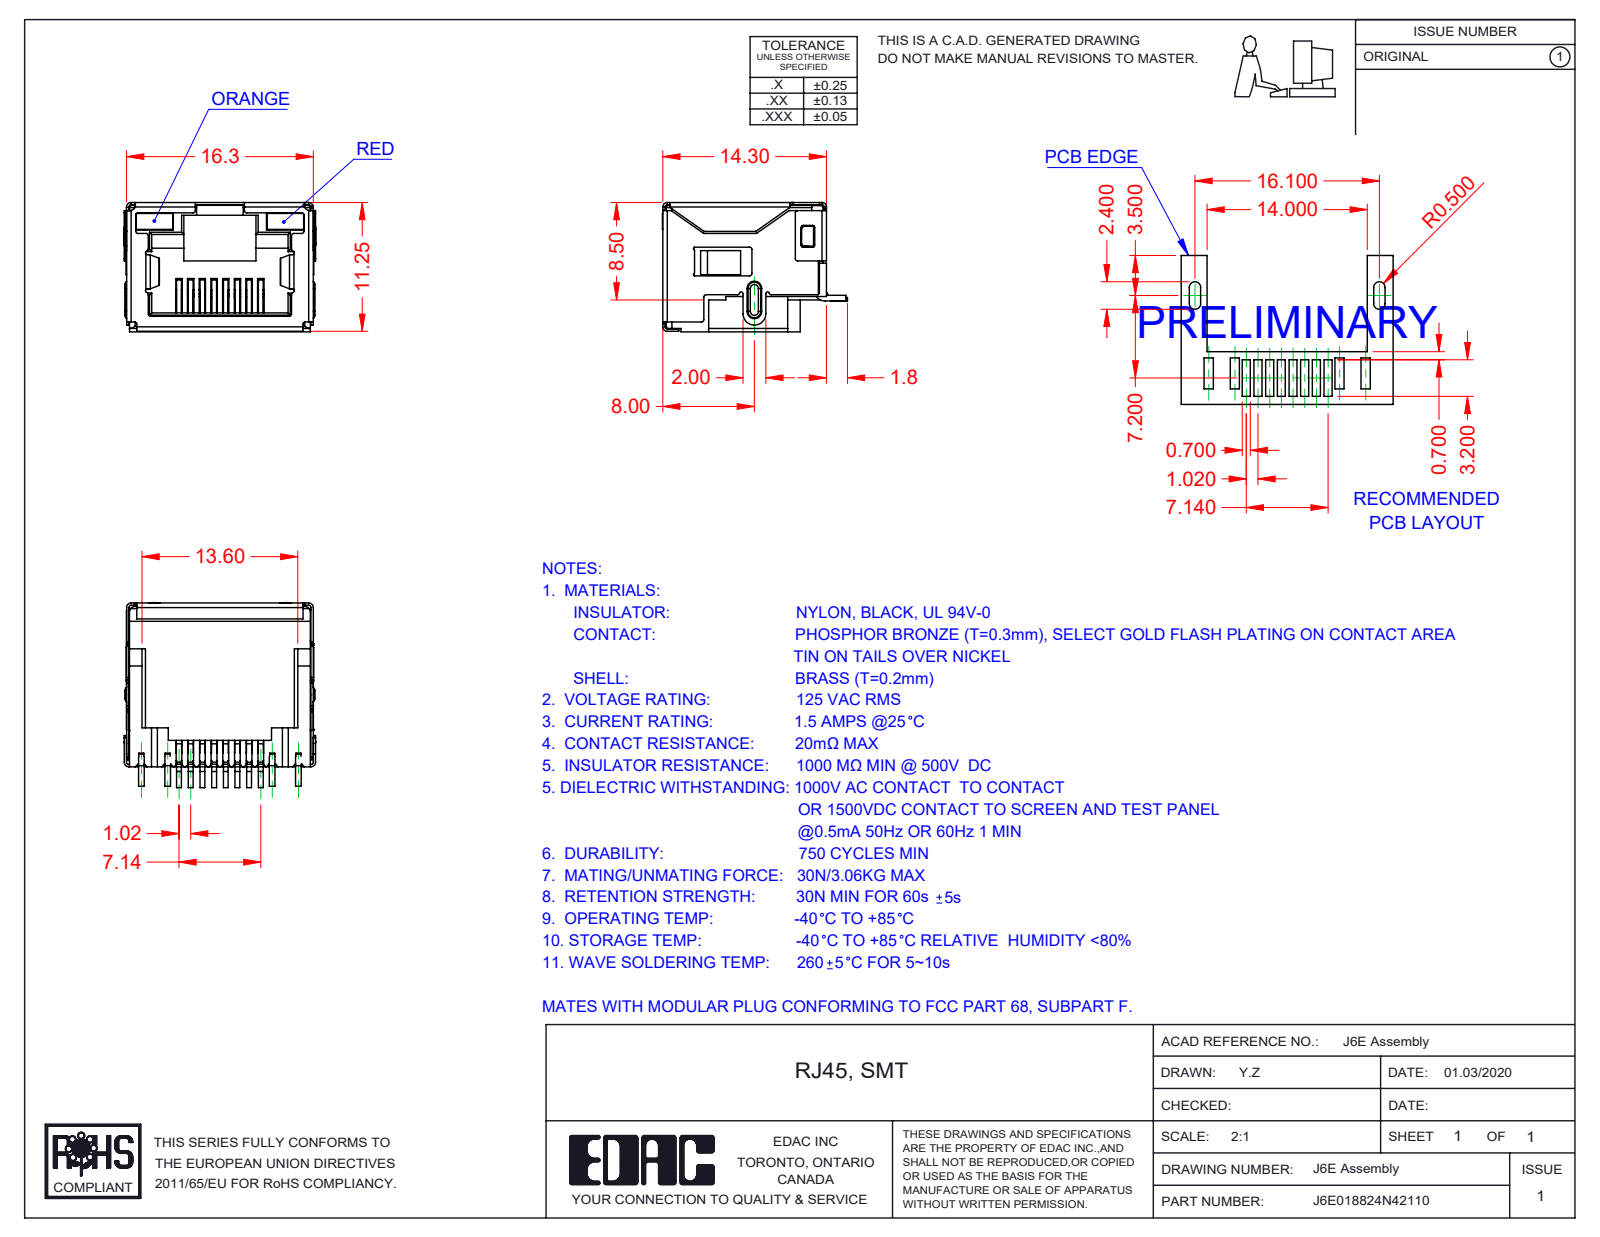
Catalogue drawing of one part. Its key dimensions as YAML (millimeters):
part_name: "6E LED LH_4-Orange; J6E018824N42110; 6E Insulator_LED; 6E Shield_LED (+2 more)"
step_written_by: "SolidWorks 2016 (CONFIG_CONTROL_DESIGN)"
units: millimeters
bodies: {solids: 12, faces: 1496, planar: 1099, cylindrical: 347, other: 50}
overall_size: [16.75, 16.15, 11.3]
volume: 1109
surface_area: 4045
partial_cylinders:
  - {radius: 0.2, count: 82}
  - {radius: 0.25, count: 17}
  - {radius: 0.4, count: 13}
  - {radius: 0.5, count: 13}
  - {radius: 0.1, count: 10}
  - {radius: 0.15, count: 7}
  - {radius: 0.3, count: 4}
  - {radius: 1, count: 3}
face_to_face_distances: [11.05, 16.05, 16.1, 15.85, 11.1, 11.3, 2.4, 0.7, 9.85, 0.49]
